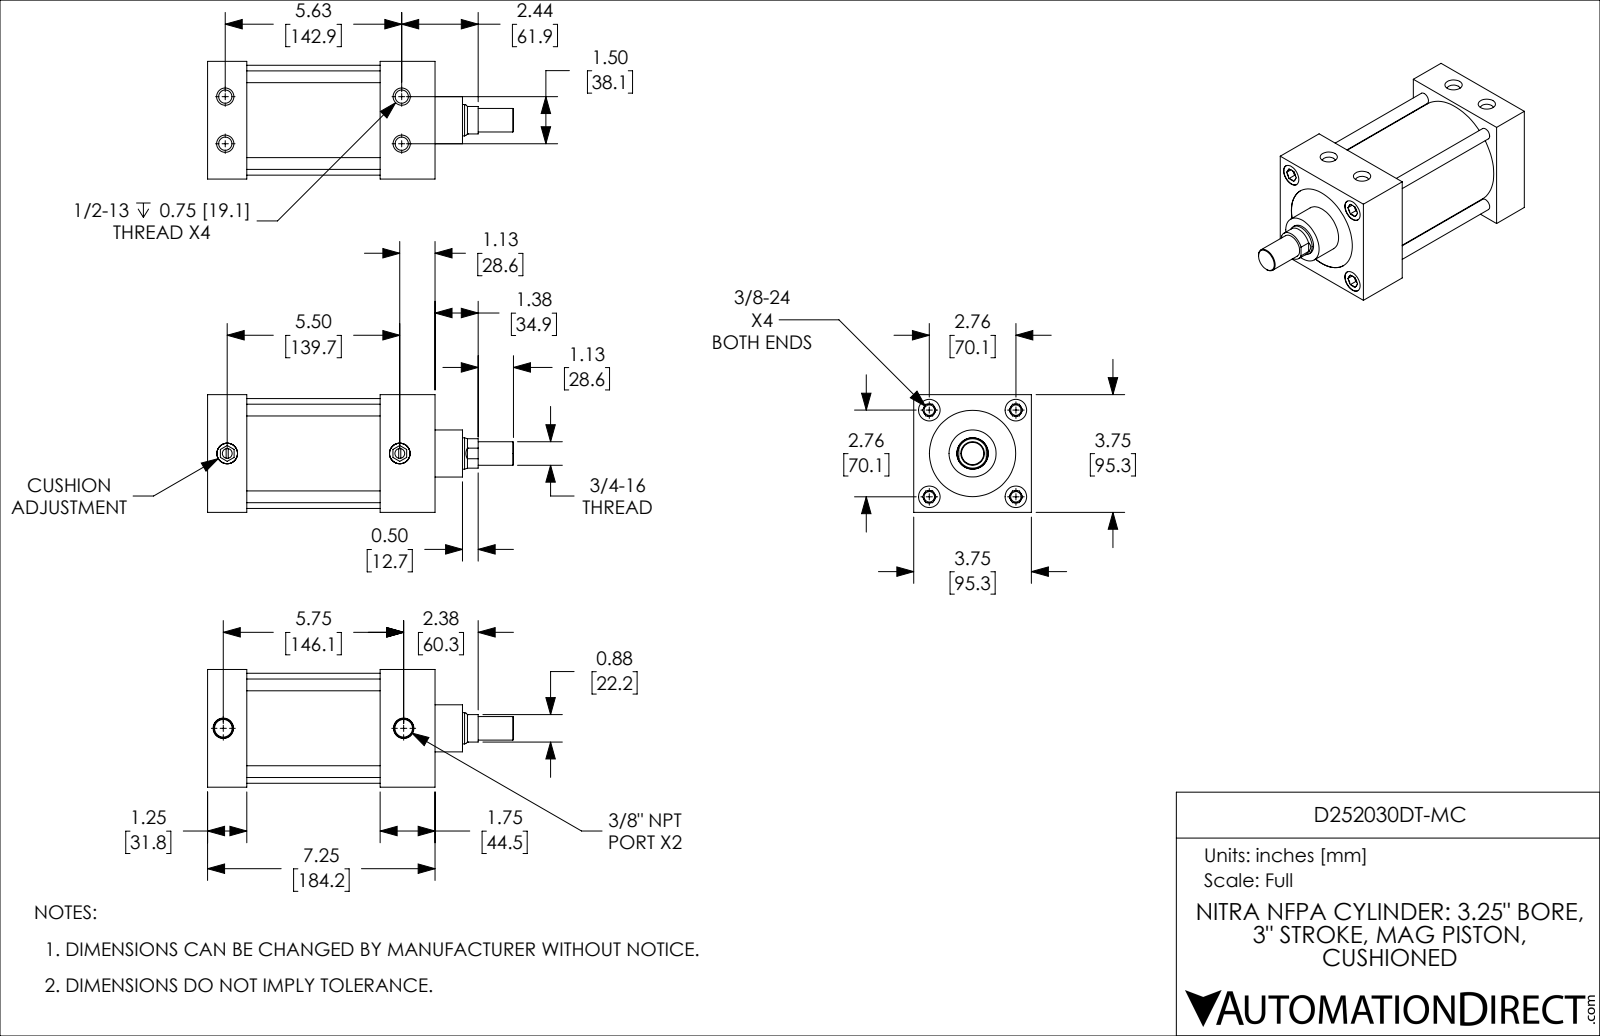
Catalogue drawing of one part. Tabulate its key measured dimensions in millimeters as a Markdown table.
| quantity | value |
| --- | --- |
| part name | D252030DT-MC_BODY; D252030DT-MC; D252030DT-MC_PISTON_KK1; D252030DT-MC_CUSHION |
| STEP written by | SolidWorks 2019 (CONFIG_CONTROL_DESIGN) |
| units | millimeters |
| bodies | 4 solids, 246 faces (90 planar, 78 cylindrical, 78 other) |
| overall size | 247.7 × 95.3 × 95.3 |
| volume | 1 024 000 mm³ |
| surface area | 189 000 mm² |
| round holes (diameter × count) | 8.4 × 4, 10.7 × 4, 17.4 × 4, 7.9 × 2, 14.3 × 2, 16.7 × 2, 25.4 × 1, 69.9 × 1, 82.6 × 1 |
| round bosses / shafts (diameter × count) | 9.5 × 4, 16.7 × 2, 88.9 × 1, 82.5 × 1, 38.1 × 1, 25.4 × 1, 19.1 × 1 |
| partial cylindrical surfaces (radius × count) | 11.9 × 1 |
| main face-to-face distances | 31.8, 95.3, 108, 139.7, 63.5, 76.2, 184.2, 152.4, 120.7, 44.5 |
| hole center spacings | 19.1, 49.6, 70.1, 145.7, 38.1, 99.1, 142.9, 147.9 |
